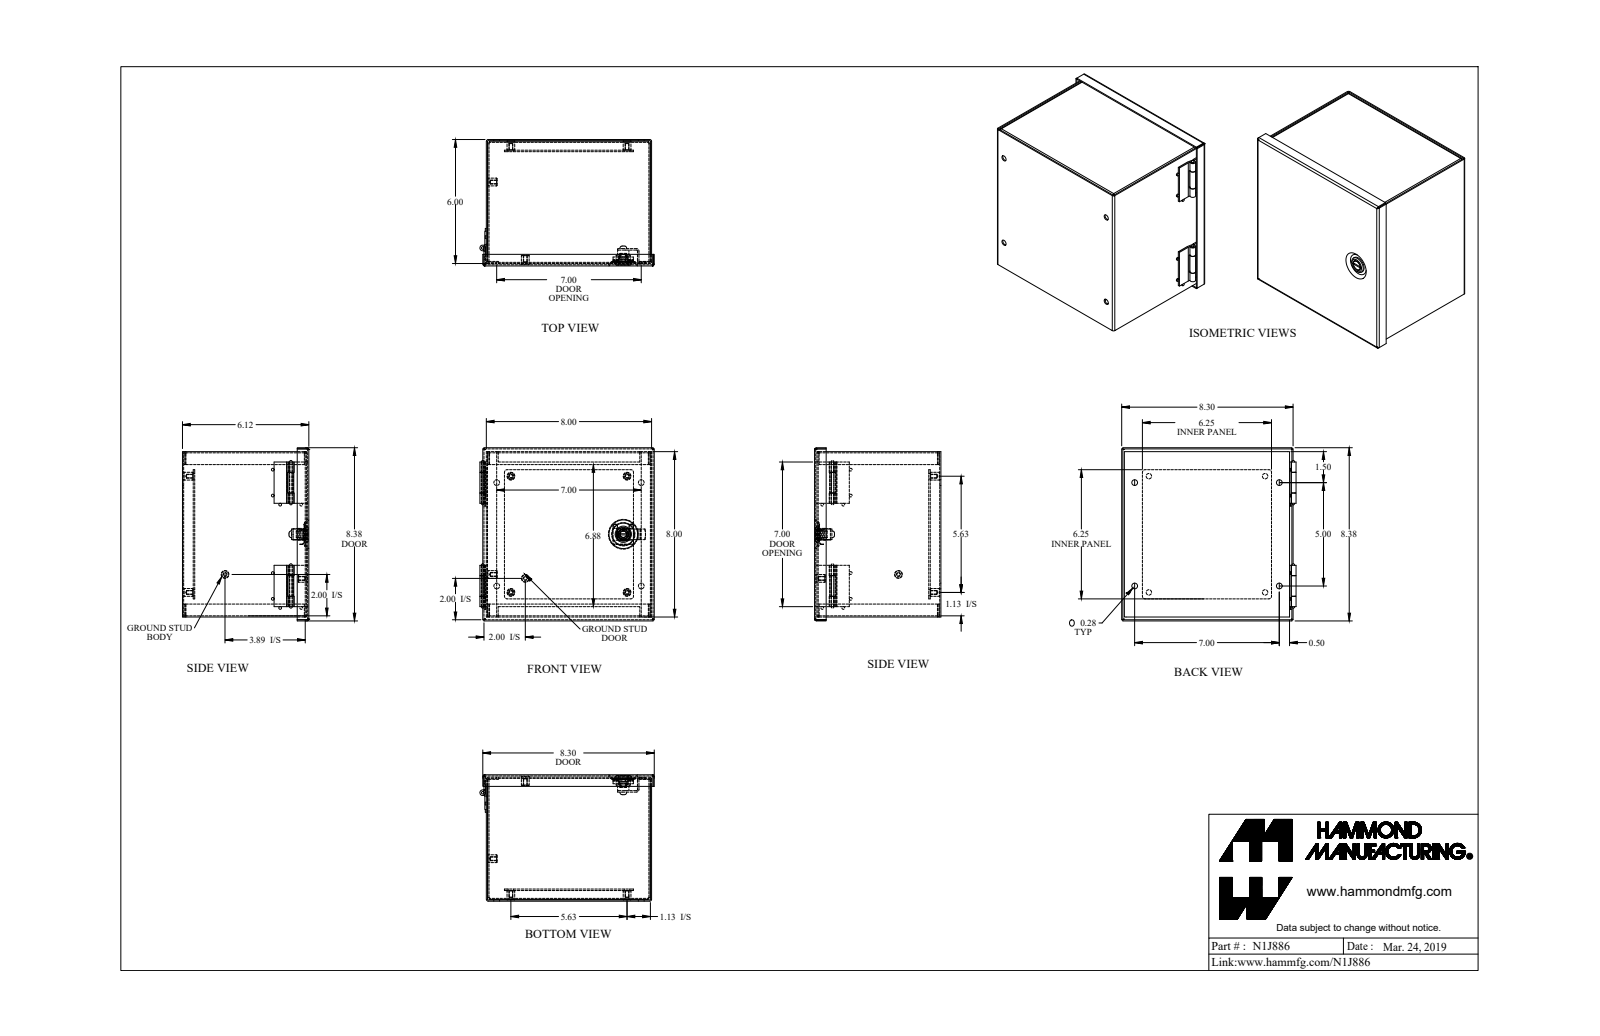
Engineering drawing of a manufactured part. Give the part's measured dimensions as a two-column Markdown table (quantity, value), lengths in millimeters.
| quantity | value |
| --- | --- |
| part name | N1J886 |
| STEP written by | SolidWorks 2018 (AUTOMOTIVE_DESIGN) |
| units | millimeters |
| bodies | 18 solids, 477 faces (224 planar, 188 cylindrical, 65 other) |
| overall size | 214.5 × 212.9 × 155.4 |
| volume | 411 200 mm³ |
| surface area | 555 700 mm² |
| round holes (diameter × count) | 4 × 6, 6.7 × 4, 7.1 × 4, 3.2 × 1, 8.1 × 1, 12.1 × 1 |
| round bosses / shafts (diameter × count) | 3.3 × 8, 9.5 × 6, 20 × 1, 13.9 × 1, 12 × 1, 11.9 × 1, 9.3 × 1, 8.1 × 1 |
| partial cylindrical surfaces (radius × count) | 0.7 × 16, 2.2 × 16, 0.3 × 4, 2.5 × 4, 3.2 × 4, 0.9 × 2, 2 × 2, 6.4 × 2 |
| main face-to-face distances | 1.4, 201.8, 153.9, 203.2, 200.3, 152.5, 155.4, 1.8, 13.1, 11.7 |
| hole center spacings | 19.2, 136.1, 142.9, 160.5, 209.6, 67.3, 71.6, 127 |
